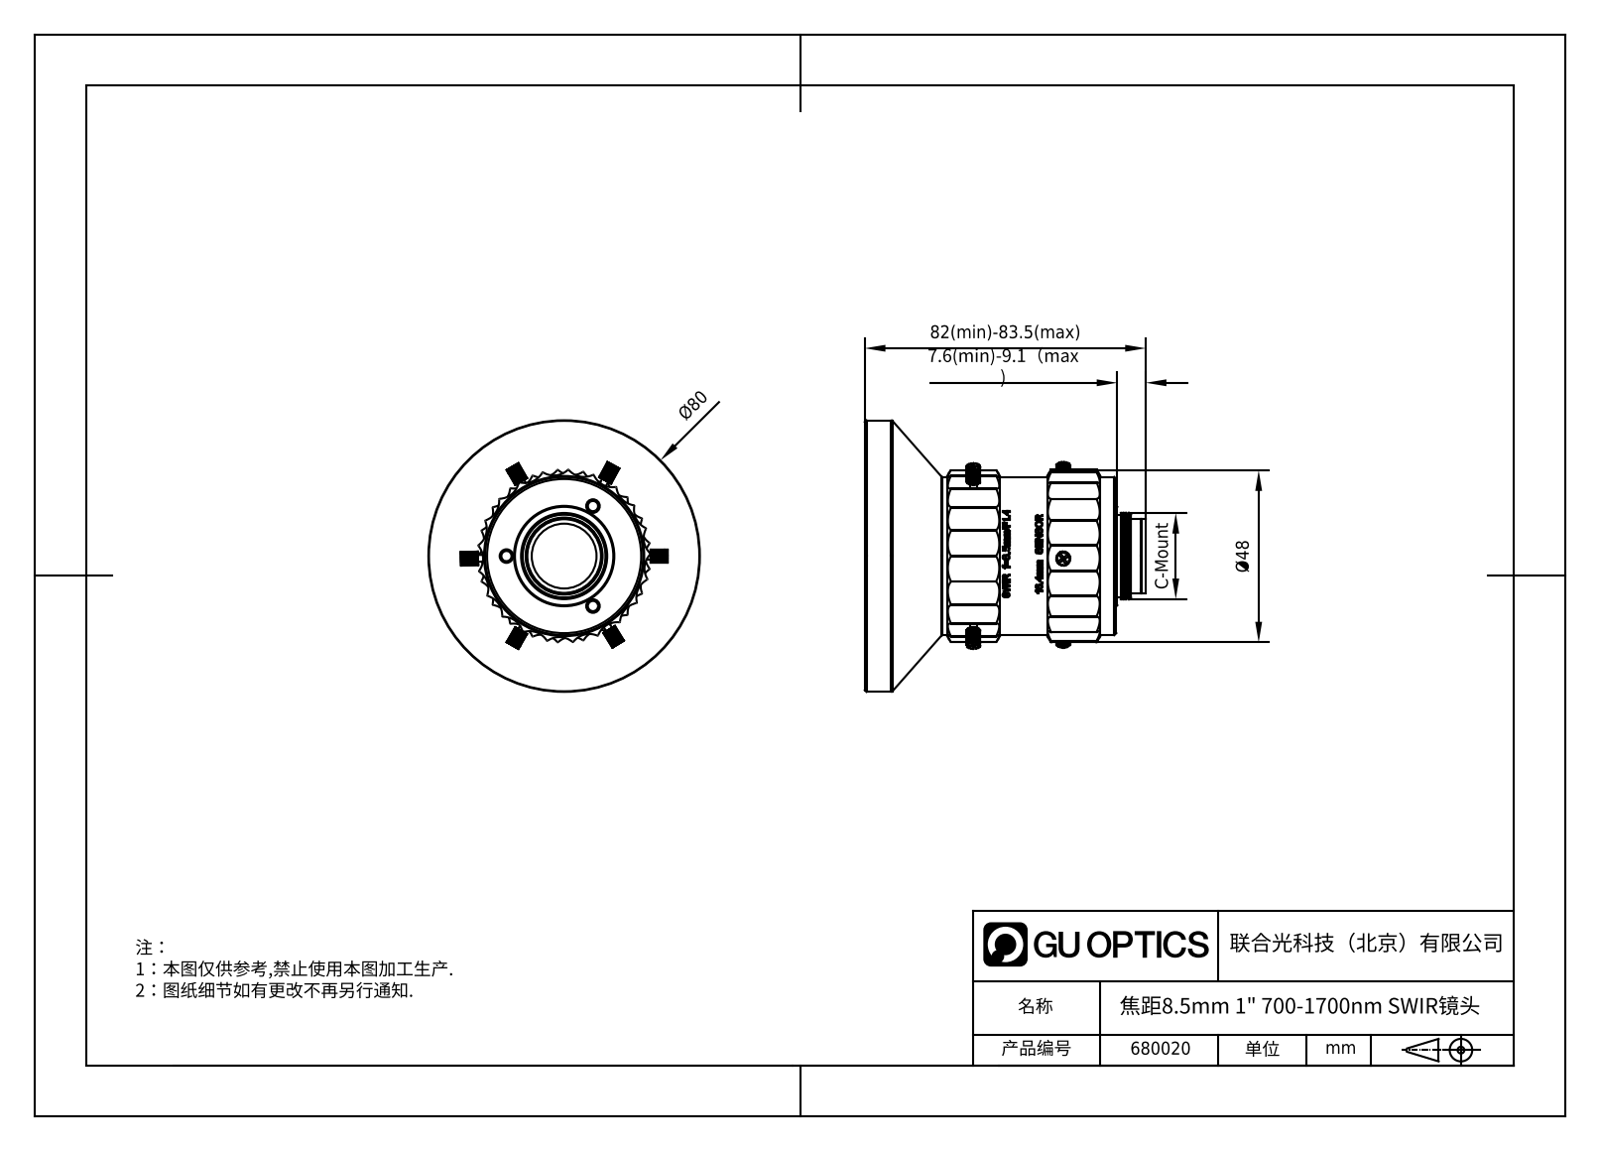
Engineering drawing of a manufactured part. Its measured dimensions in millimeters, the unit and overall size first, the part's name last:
Units: millimetres
Overall size (bounding box): 82.81 × 80 × 80
Round holes (diameter × count): ⌀1.6 ×11, ⌀1.2 ×8, ⌀1.1 ×5, ⌀3 ×4, ⌀0.9 ×3, ⌀1.4 ×3, ⌀1.64 ×3, ⌀2.1 ×3, ⌀2.2 ×3, ⌀4 ×3, ⌀1 ×2, ⌀1.3 ×1
Round bosses / shafts (diameter × count): ⌀2 ×9, ⌀1.2 ×8, ⌀2.5 ×6, ⌀1.4 ×6, ⌀3.6 ×3, ⌀3.2 ×3, ⌀80 ×1, ⌀46.6 ×1
Partial cylindrical surfaces — rounded edges, fillets, slot ends (radius × count): R0.2 ×42, R1 ×42, R6 ×42, R0.5 ×19, R1.5 ×18, R14.5 ×9, R0.6 ×8, R10.25 ×8
Main face-to-face distances: 13.31, 1.4, 13.25, 20.79, 20.85, 34.1, 10.1, 30.89, 30.95, 44.2
Hole centre spacings: 9.49, 12.4, 17.54, 22.91, 24.8, 17, 23.8, 29.44
Volume: 96 842 mm³ · Surface area: 76 374 mm²
Bodies: 49 solids, 2119 faces (1009 planar, 677 cylindrical, 433 other)
Part name (STEP PRODUCT): 680020
STEP written by: SolidWorks 2020 (CONFIG_CONTROL_DESIGN)
